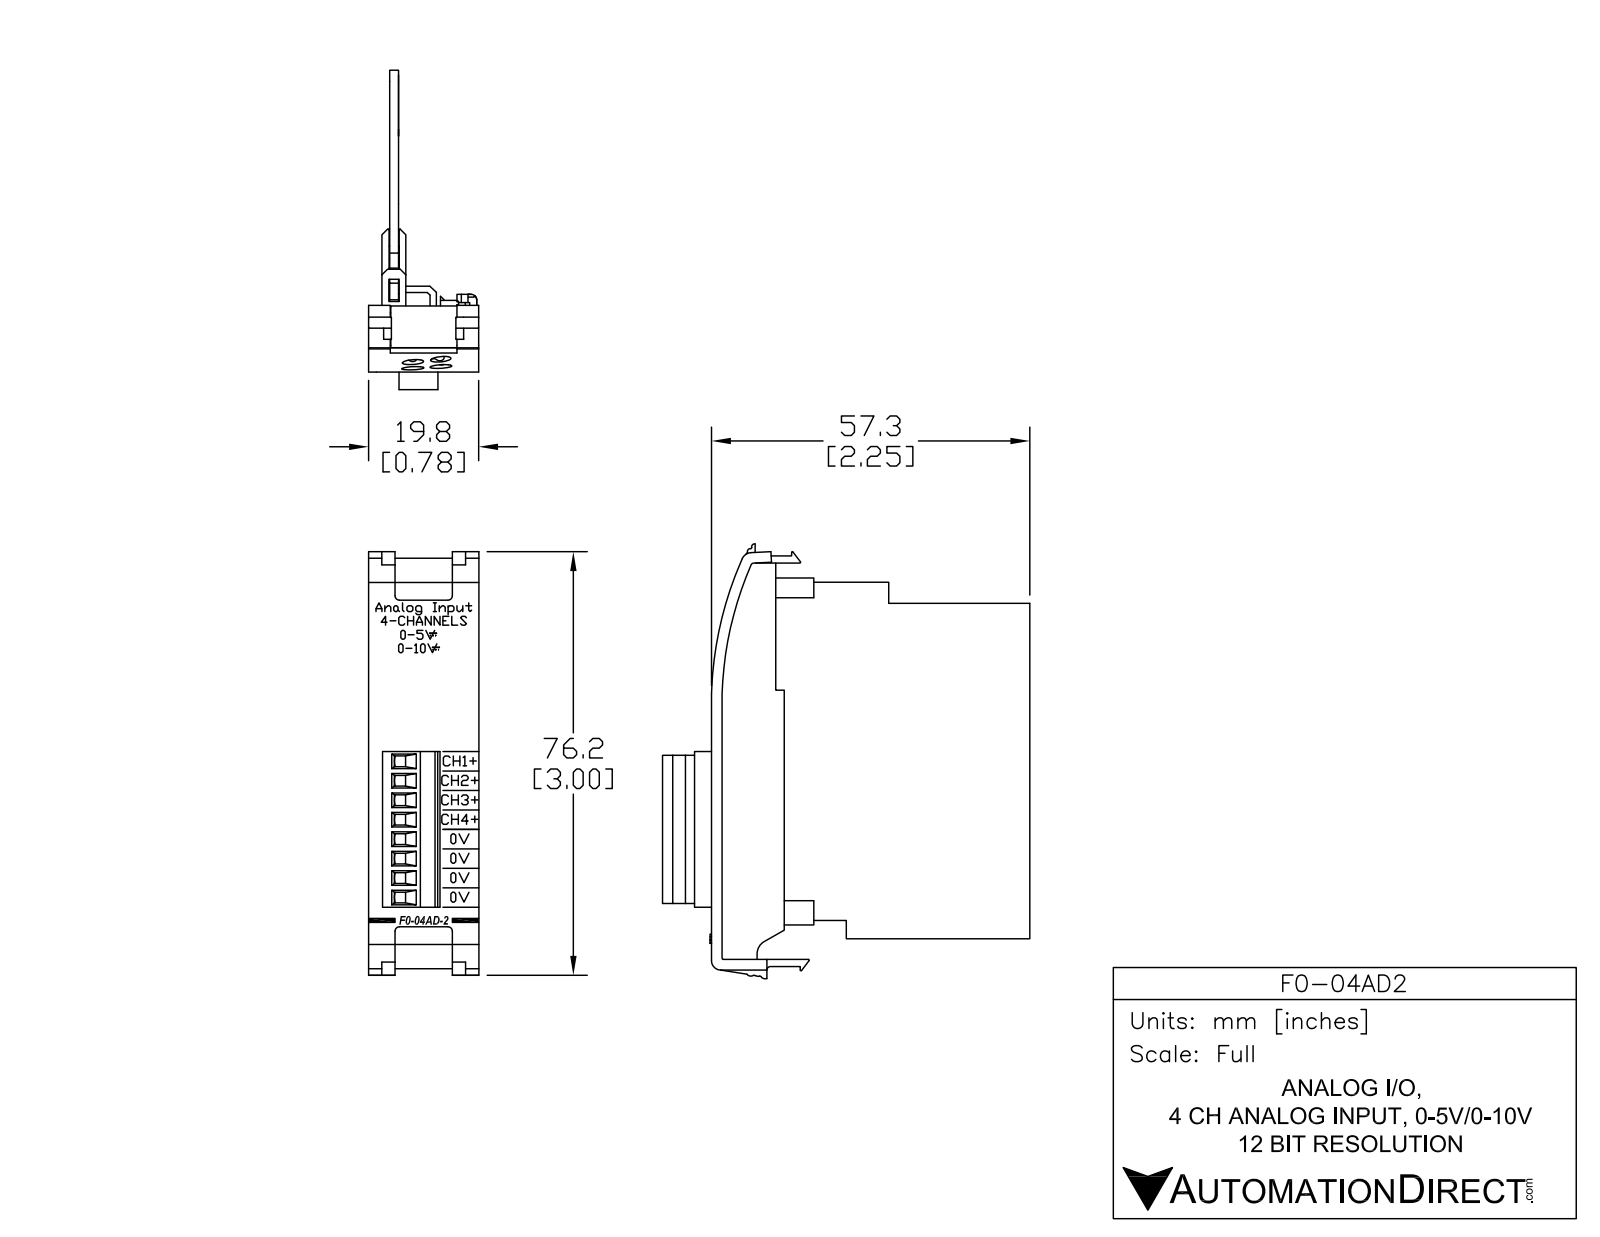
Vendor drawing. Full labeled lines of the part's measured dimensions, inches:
Part name (STEP PRODUCT): F0-04AD-2
STEP written by: SolidWorks 2009 (AUTOMOTIVE_DESIGN)
Units: inches
Bodies: 2 solids, 314 faces (248 planar, 35 cylindrical, 31 other)
Overall size (bounding box): 3.08 × 2.602 × 0.826
Volume: 0.734 in³ · Surface area: 22.8 in²
Partial cylindrical surfaces — rounded edges, fillets, slot ends (radius × count): R0.005 ×4, R0.02 ×3, R0.035 ×3, R0.025 ×2, R0.01 ×1, R0.065 ×1, R0.07 ×1, R0.1 ×1
Main face-to-face distances: 0.063, 0.631, 0.05, 0.075, 0.113, 0.581, 0.519, 0.681, 0.569, 0.195
